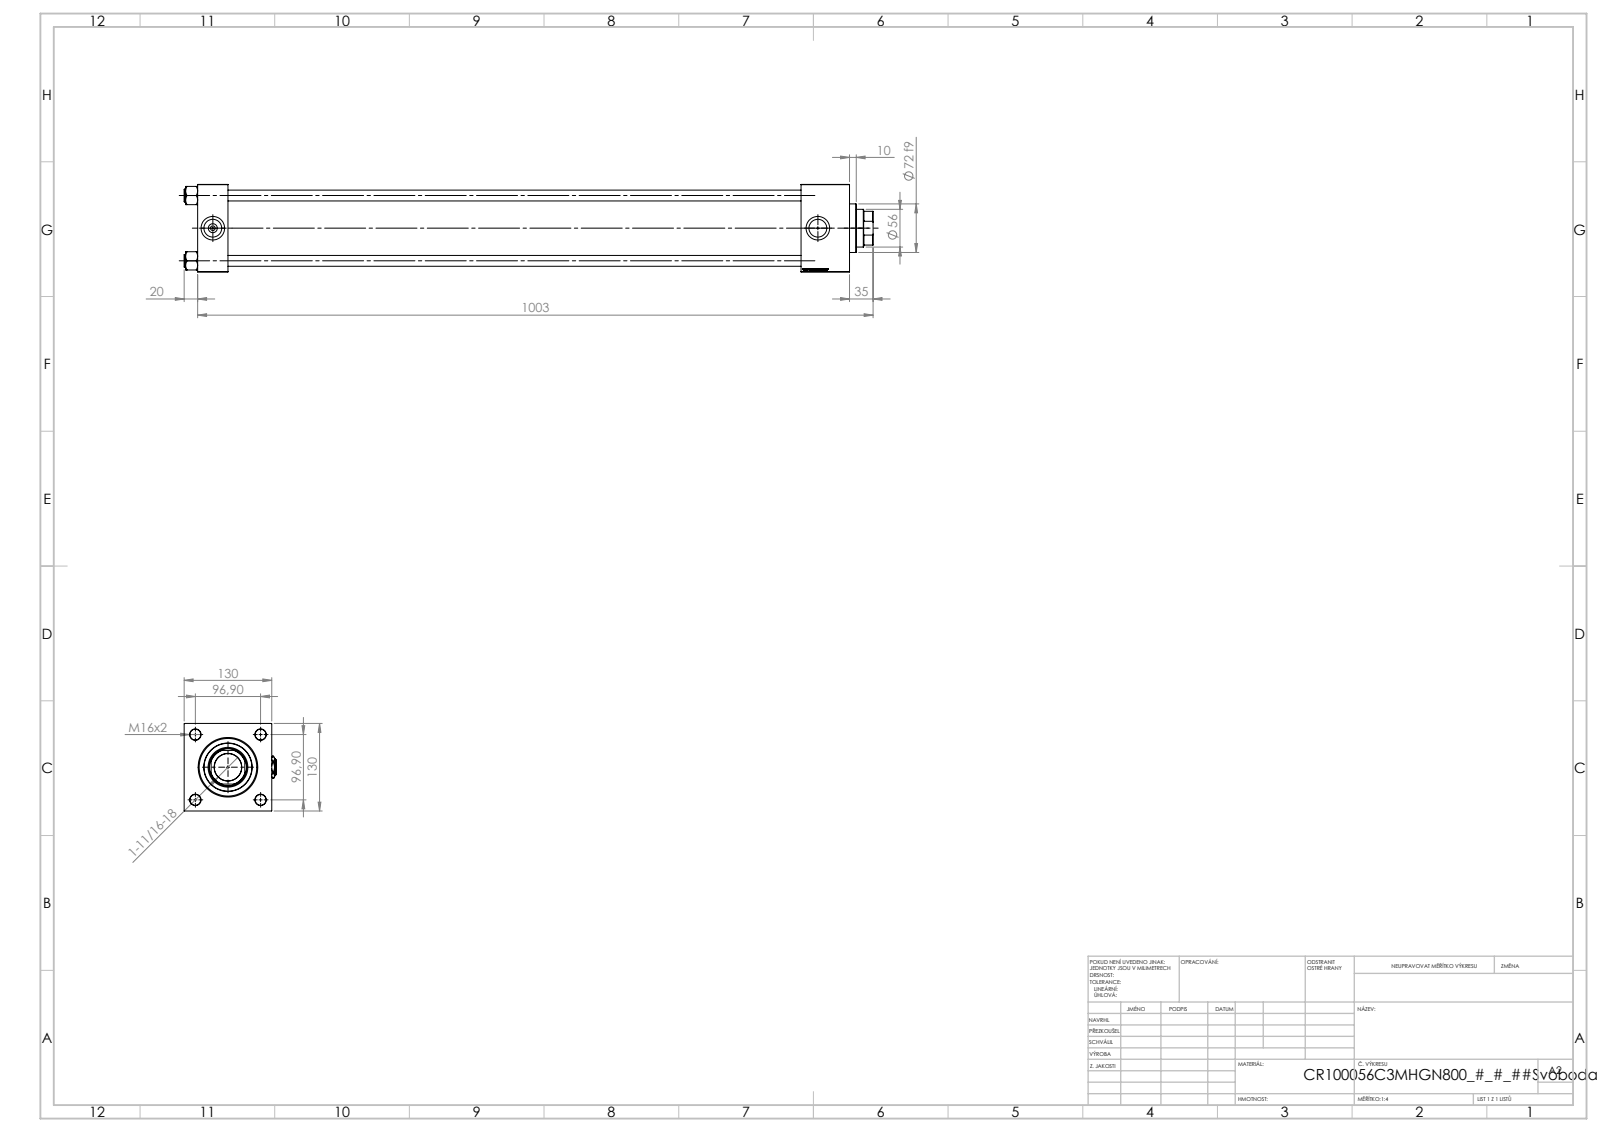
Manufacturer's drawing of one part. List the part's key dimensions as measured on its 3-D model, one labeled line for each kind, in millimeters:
Part name (STEP PRODUCT): NUT_M5_C; V215CR_C_Body; Zatka_pro_OIL_PORT; V215CR_C_TYCINKA (+2 more)
STEP written by: SolidWorks 2019 (CONFIG_CONTROL_DESIGN)
Units: millimetres
Bodies: 13 solids, 1297 faces (621 planar, 98 cylindrical, 578 other)
Overall size (bounding box): 1023 × 137 × 130
Volume: 5 767 000 mm³ · Surface area: 1 139 000 mm²
Round holes (diameter × count): ⌀16 ×4, ⌀7 ×2, ⌀26.44 ×2, ⌀35 ×2, ⌀40.5 ×1, ⌀56 ×1, ⌀59 ×1, ⌀76 ×1, ⌀85.5 ×1, ⌀100 ×1
Round bosses / shafts (diameter × count): ⌀19 ×4, ⌀106 ×1, ⌀72 ×1
Partial cylindrical surfaces — rounded edges, fillets, slot ends (radius × count): R27 ×1
Main face-to-face distances: 130, 45, 968, 923, 896, 851, 72, 51, 872, 96
Hole centre spacings: 68.52, 96.9, 137.04, 898.5
